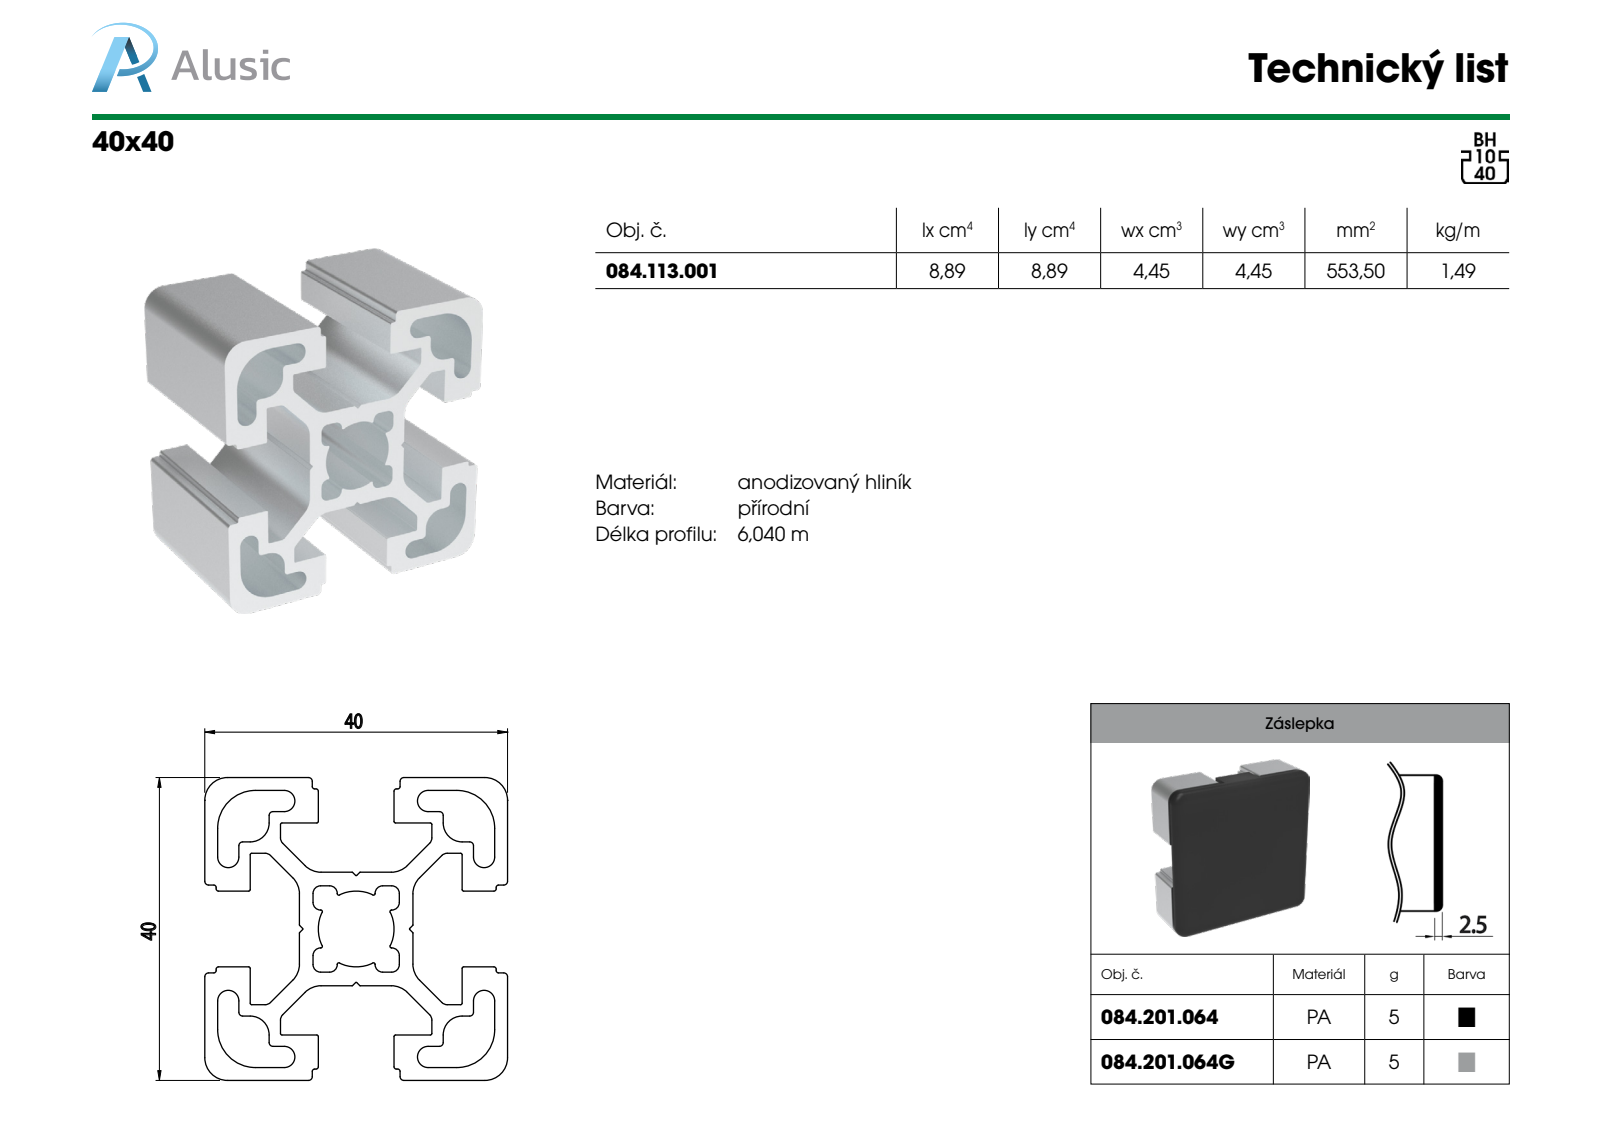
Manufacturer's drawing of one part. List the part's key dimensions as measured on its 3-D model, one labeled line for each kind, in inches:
Part name (STEP PRODUCT): 084.113.001
STEP written by: SolidWorks 2018 (AUTOMOTIVE_DESIGN)
Units: inches
Bodies: 1 solid, 240 faces (114 planar, 126 cylindrical, 0 other)
Overall size (bounding box): 3.937 × 1.575 × 1.575
Volume: 3.378 in³ · Surface area: 79.18 in²
Partial cylindrical surfaces — rounded edges, fillets, slot ends (radius × count): R0.008 ×24, R0.039 ×20, R0.012 ×16, R0.02 ×16, R0.004 ×12, R0.118 ×12, R0.055 ×8, R0.197 ×5
Main face-to-face distances: 0.492, 0.591, 0.098, 1.575, 0.846, 0.256, 0.748, 0.169, 0.236, 1.339
